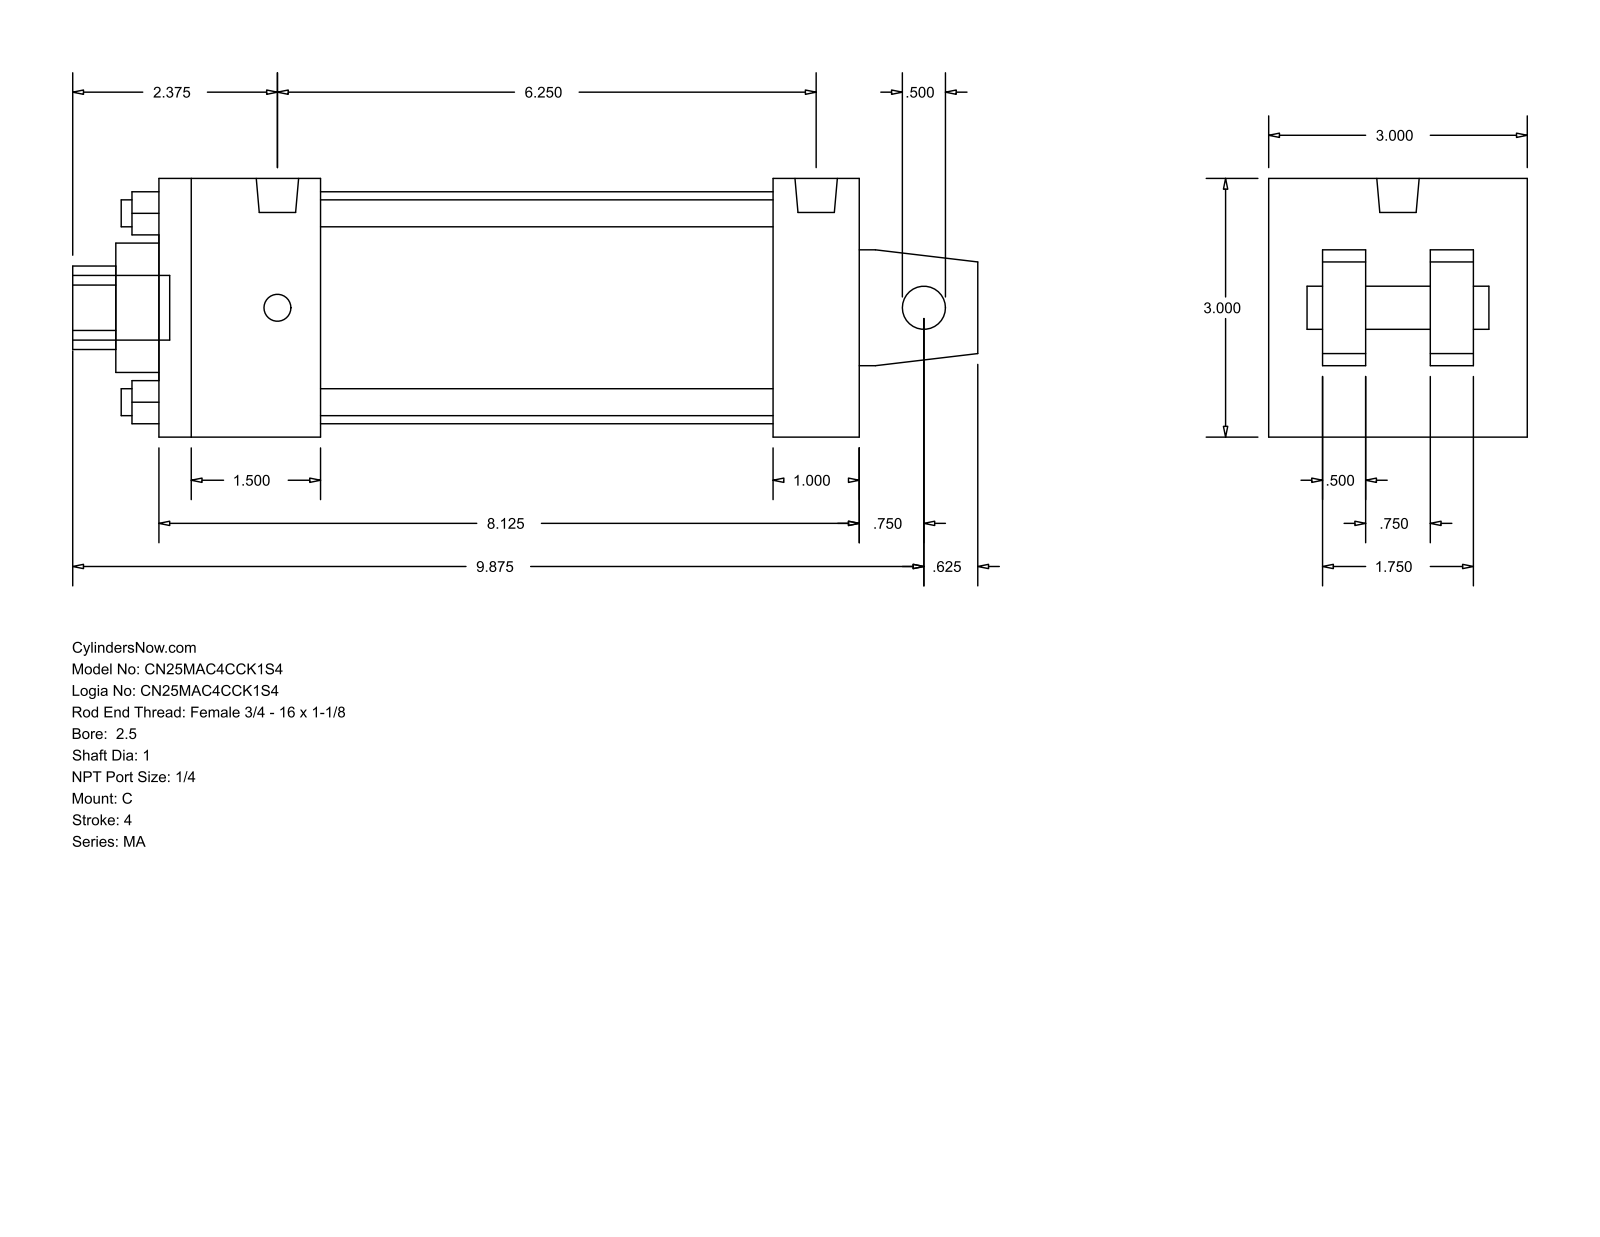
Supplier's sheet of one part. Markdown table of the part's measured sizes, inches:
| quantity | value |
| --- | --- |
| part name | MA_C__0250_1 |
| STEP written by | GSSL Pune (CONFIG_CONTROL_DESIGN) |
| units | inches |
| bodies | 0 solids, 103 faces (76 planar, 27 cylindrical, 0 other) |
| overall size | 10.5 × 3 × 3 |
| round holes (diameter × count) | 0.313 × 4, 0.5 × 1, 1 × 1, 1.5 × 1, 2.69 × 1 |
| round bosses / shafts (diameter × count) | 0.313 × 4, 0.492 × 2, 0.75 × 1 |
| partial cylindrical surfaces (radius × count) | 0.484 × 1 |
| main face-to-face distances | 3, 8.125, 1.875, 0.5, 0.625, 2.375, 1, 1.125, 7.125, 5.25 |
| hole center spacings | 1.548, 2.19, 3.097 |
